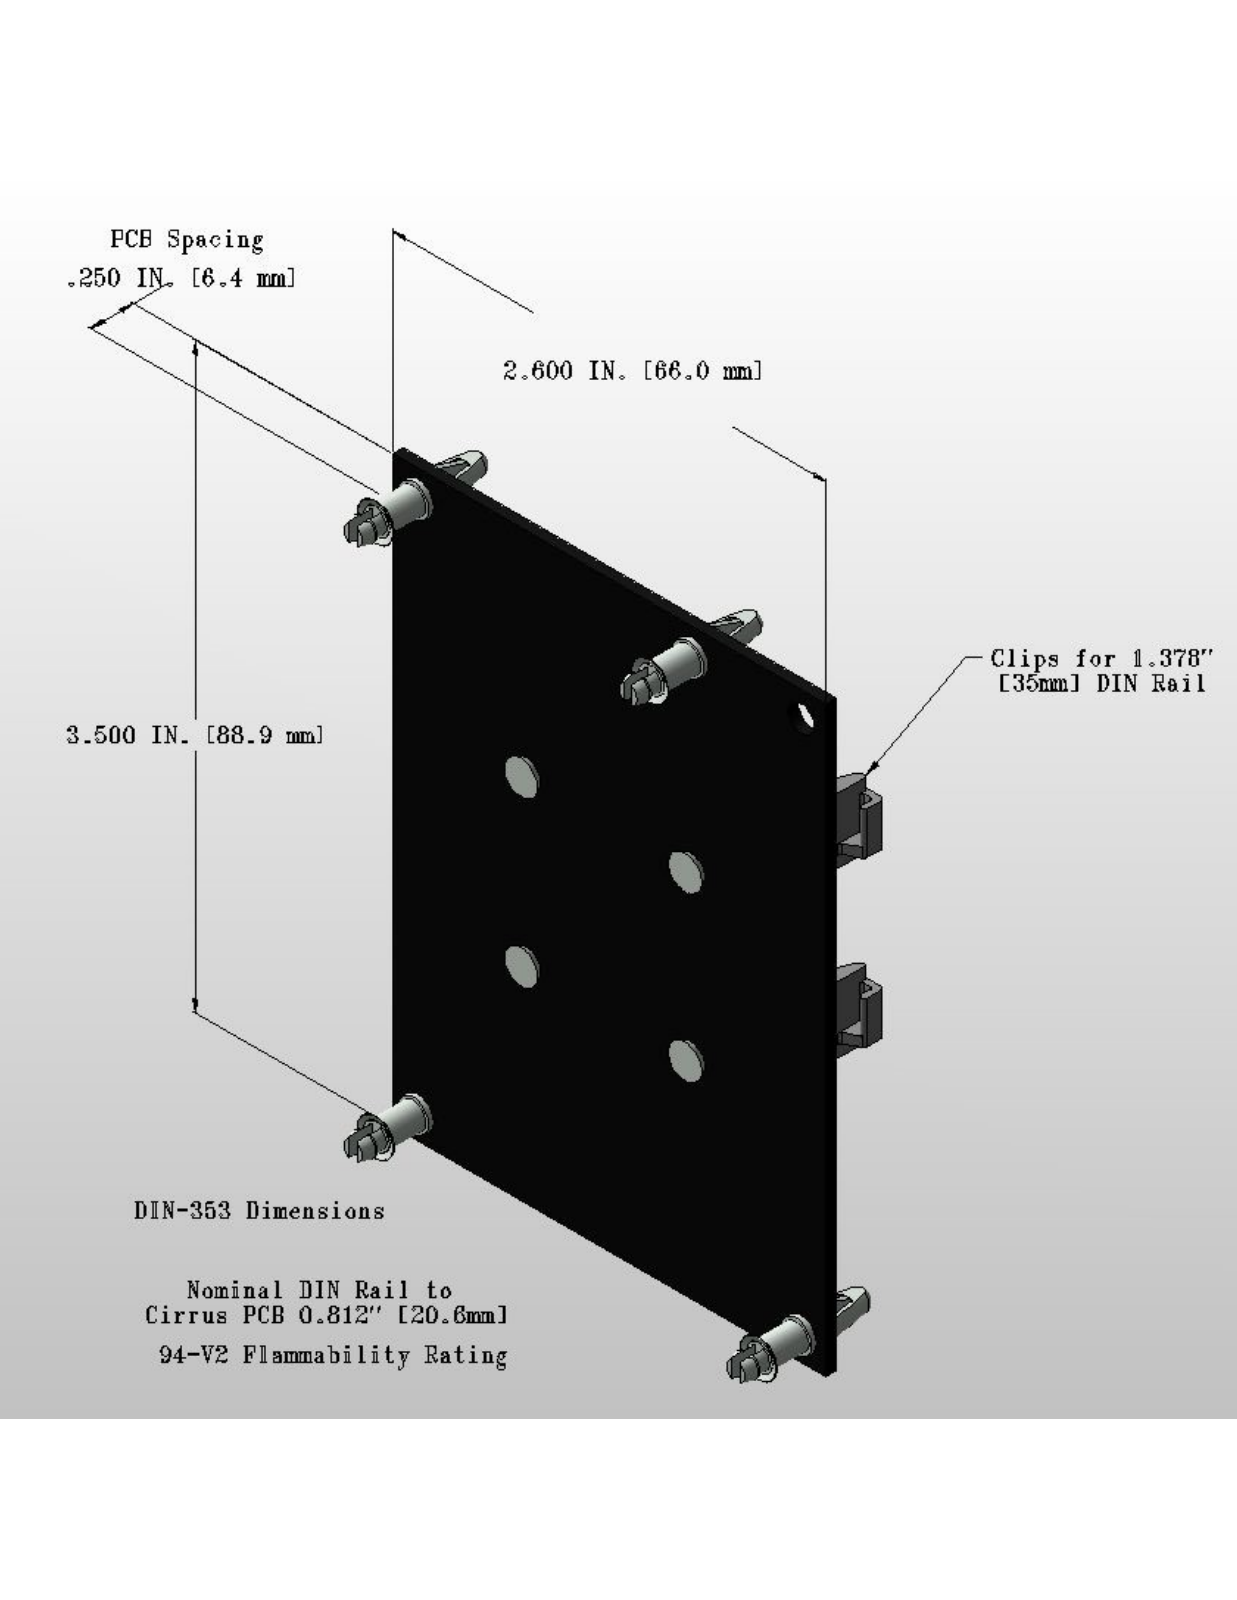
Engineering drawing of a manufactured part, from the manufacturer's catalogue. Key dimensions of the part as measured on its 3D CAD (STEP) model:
STEP written by: KeyCreator Pro (AP242_MANAGED_MODEL_BASED_3D_ENGINEERING_MIM_LF)
Units: inches
Bodies: 11 solids, 537 faces (310 planar, 187 cylindrical, 40 other)
Overall size (bounding box): 3.5 × 2.6 × 1.2
Volume: 0.947 in³ · Surface area: 33.75 in²
Round holes (diameter × count): ⌀0.156 ×9, ⌀0.108 ×6, ⌀0.079 ×1, ⌀0.118 ×1
Round bosses / shafts (diameter × count): ⌀0.218 ×4, ⌀0.187 ×4, ⌀0.154 ×4
Partial cylindrical surfaces — rounded edges, fillets, slot ends (radius × count): R0.016 ×20, R0.02 ×6, R0.039 ×6, R0.128 ×6, R0.061 ×4, R0.071 ×4, R0.079 ×4, R0.02 ×3
Main face-to-face distances: 0.062, 0.053, 0.984, 0.357, 0.295, 0.115, 0.242, 0.394, 0.984, 0.057
Hole centre spacings: 0.984, 0.492, 1.1, 1.289, 1.597, 1.981, 2.193, 2.387
